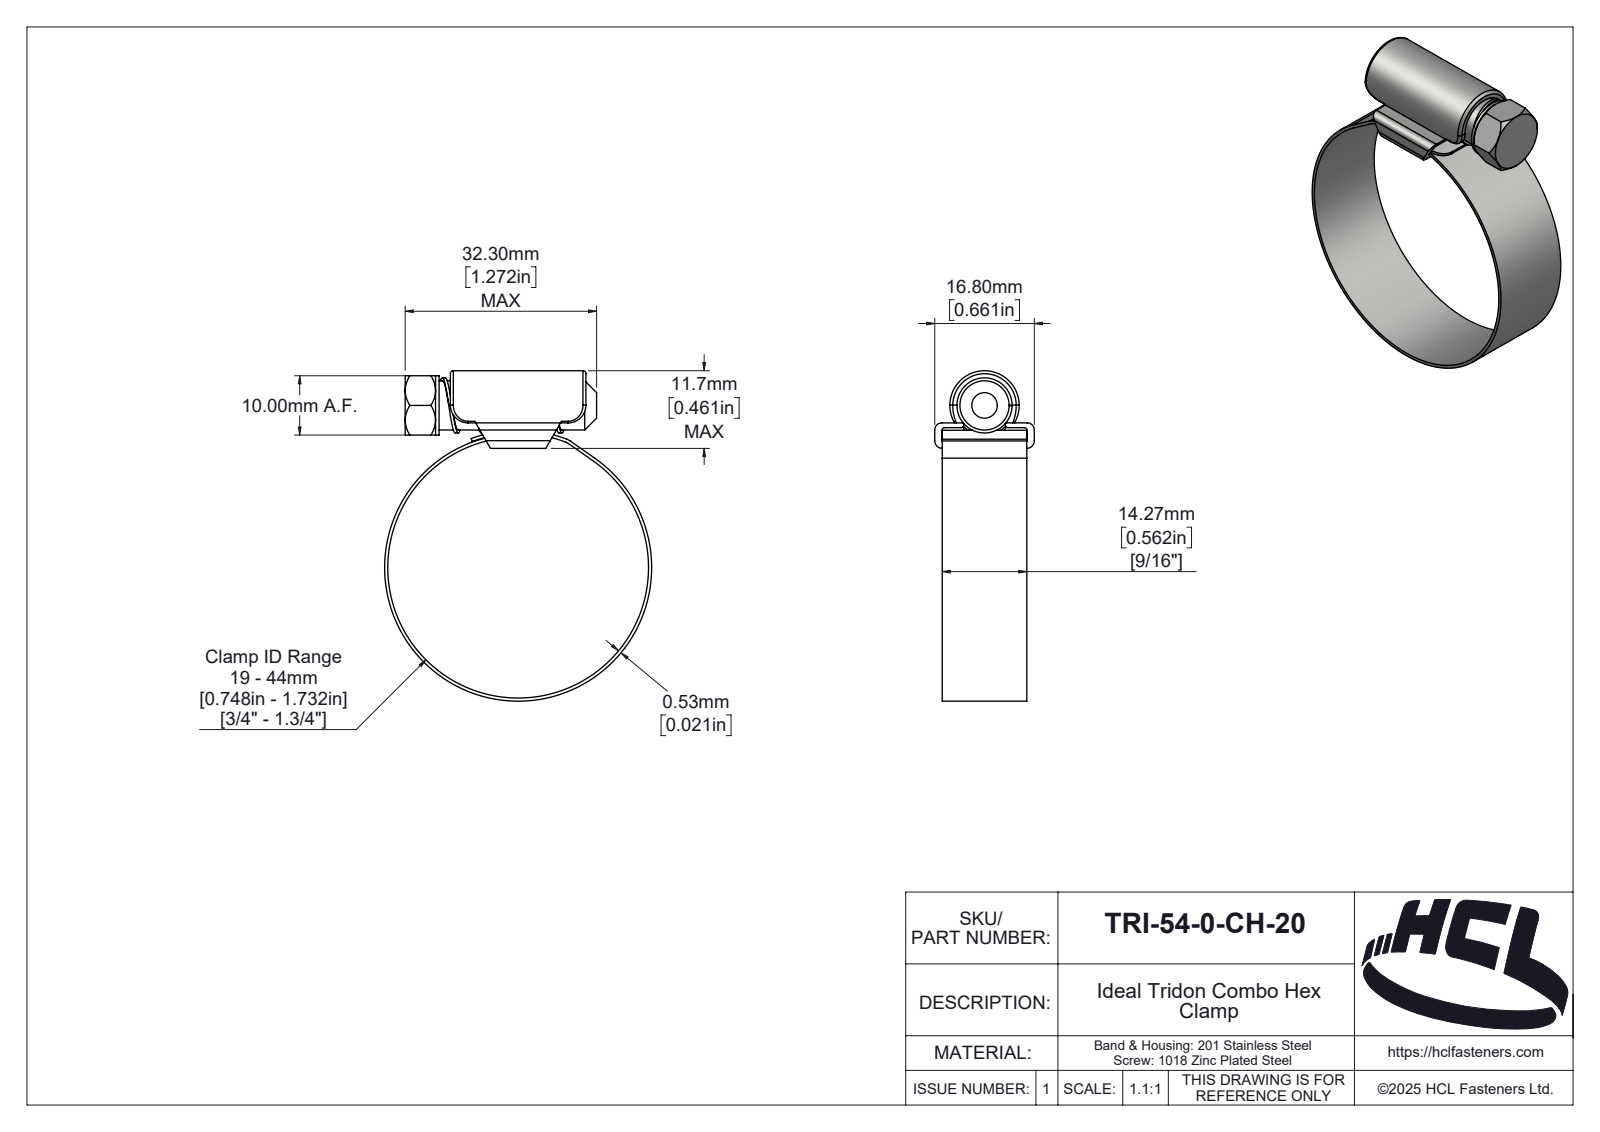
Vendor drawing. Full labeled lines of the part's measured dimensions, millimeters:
Part name (STEP PRODUCT): TRI-54-0-CH-20
STEP written by: SolidWorks 2025 (AUTOMOTIVE_DESIGN)
Units: millimetres
Bodies: 3 solids, 212 faces (35 planar, 101 cylindrical, 76 other)
Overall size (bounding box): 55.73 × 45.06 × 16.8
Volume: 4 006 mm³ · Surface area: 7 370 mm²
Round holes (diameter × count): ⌀44 ×1
Round bosses / shafts (diameter × count): ⌀45.06 ×1, ⌀10 ×1, ⌀8.3 ×1
Partial cylindrical surfaces — rounded edges, fillets, slot ends (radius × count): R0.5 ×6, R3 ×4, R0.1 ×2, R1.2 ×2, R1.3 ×2, R0.46 ×1, R1.89 ×1, R2 ×1
Main face-to-face distances: 1.2, 14.26, 3.5, 2.3, 0.53, 4.3, 3.1, 0.8, 9.99, 1.27
